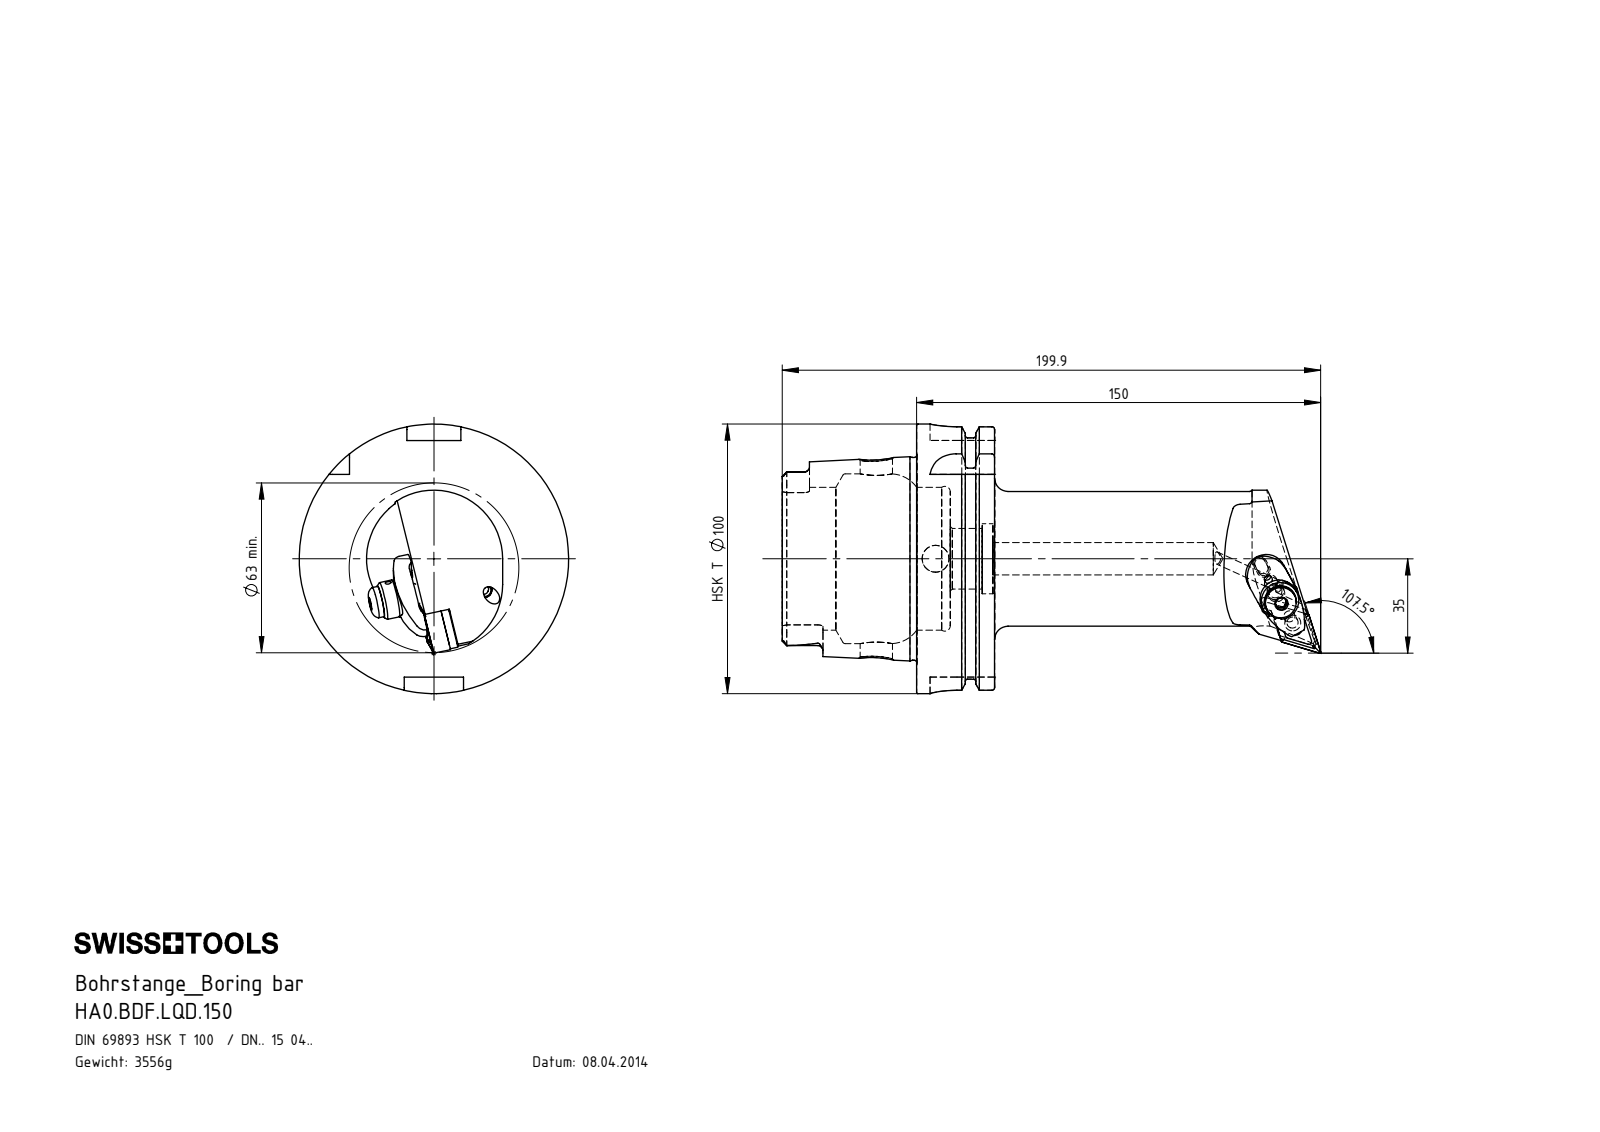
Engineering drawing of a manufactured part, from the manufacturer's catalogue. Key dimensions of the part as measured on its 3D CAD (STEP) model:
Part name (STEP PRODUCT): HA0.BDF.LQD.150; KVT_MB_600_050; WCC-ER5.102.012_B; WCC-ER3.102.024_C (+6 more)
STEP written by: SolidWorks 2022 (AUTOMOTIVE_DESIGN)
Units: millimetres
Bodies: 10 solids, 449 faces (114 planar, 149 cylindrical, 186 other)
Overall size (bounding box): 199.9 × 100 × 100
Volume: 454 008 mm³ · Surface area: 75 962 mm²
Round holes (diameter × count): ⌀2 ×3, ⌀4.2 ×2, ⌀5 ×2, ⌀7 ×2, ⌀12 ×2, ⌀3 ×1, ⌀4 ×1, ⌀5.16 ×1, ⌀6.2 ×1, ⌀6.5 ×1, ⌀8.5 ×1, ⌀10 ×1
Round bosses / shafts (diameter × count): ⌀5 ×2, ⌀100 ×1, ⌀91.95 ×1, ⌀75.26 ×1, ⌀50 ×1, ⌀14 ×1, ⌀11.5 ×1, ⌀7 ×1
Partial cylindrical surfaces — rounded edges, fillets, slot ends (radius × count): R0.39 ×6, R0.69 ×6, R1.9 ×6, R0.4 ×4, R10 ×4, R1.5 ×3, R3 ×3, R2 ×2
Main face-to-face distances: 28.95, 12.45, 16.5, 49.9, 62.35, 78.85, 87.8, 78.2, 28.3, 15.85
Hole centre spacings: 7.99, 8.03, 8.2, 14.81, 14.98, 15.02, 23.01
